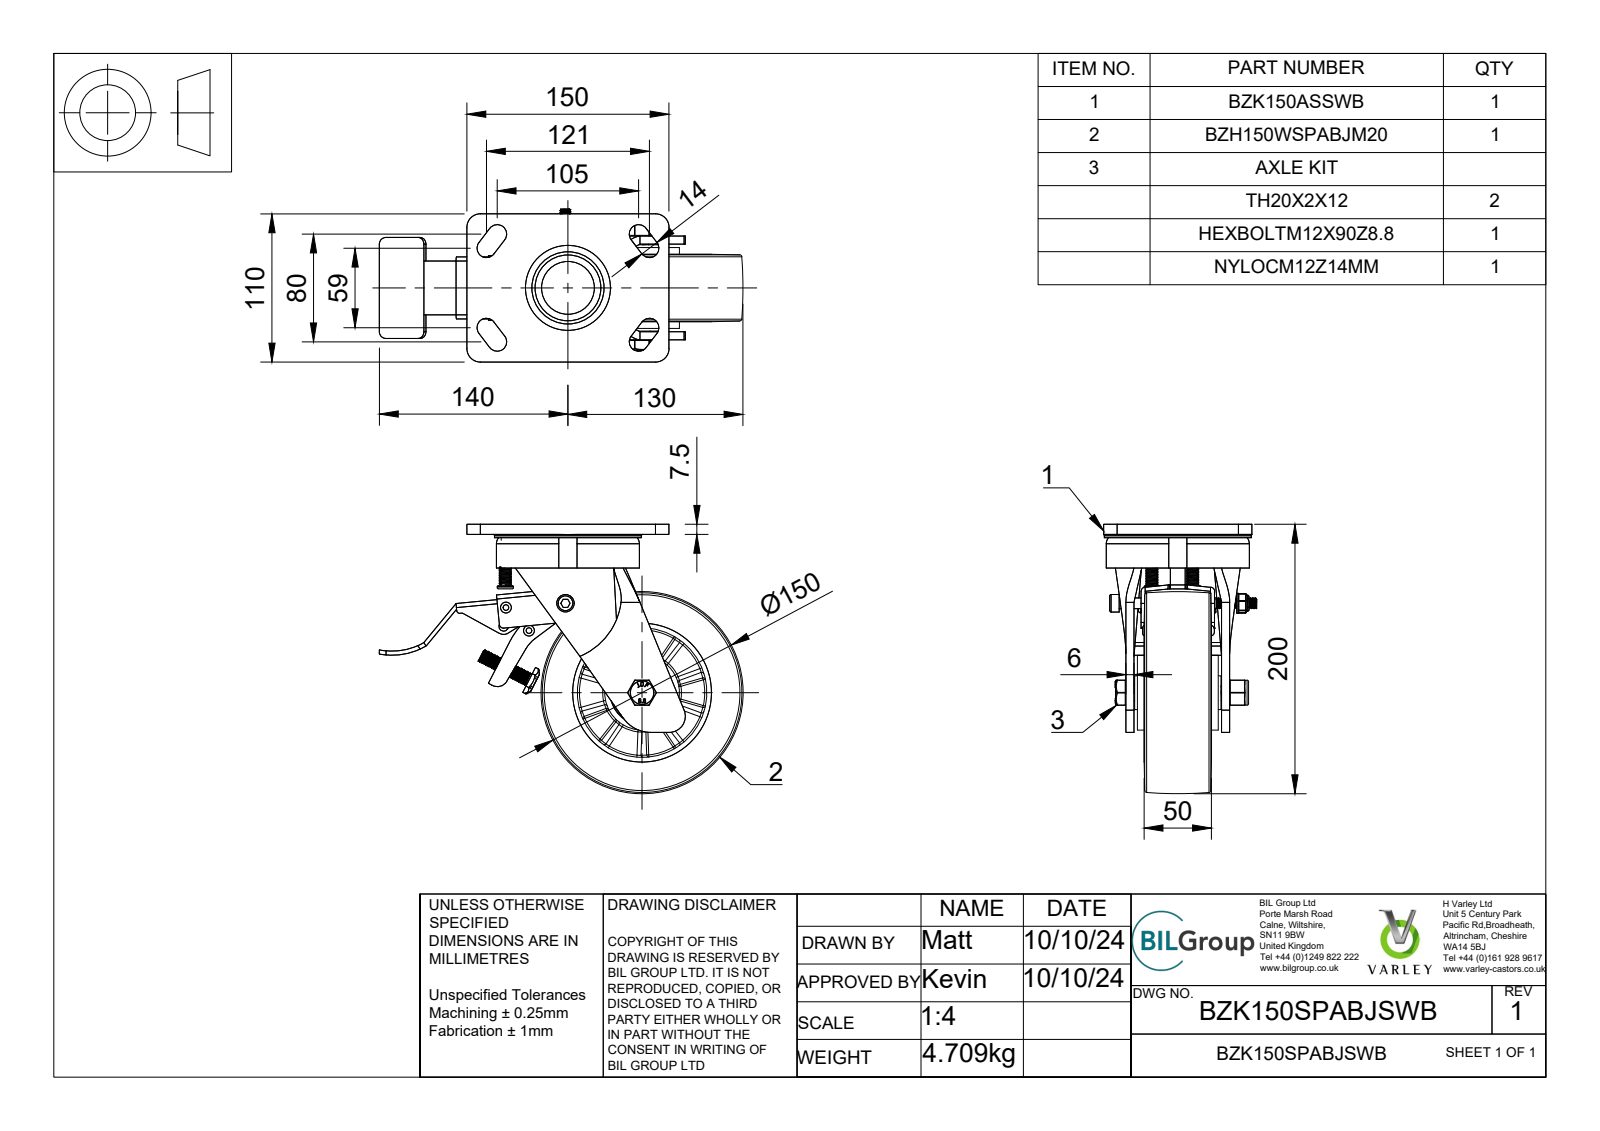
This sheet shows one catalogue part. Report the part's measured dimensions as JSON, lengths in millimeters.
{"part_name": "BZK150SPABJSWB v5; BZK150ASSWB v2; FABRICATED STEEL TOP PLATE; FABRICATED STEEL FORKS (+8 more)", "step_written_by": "Autodesk Translation Framework v13.20.0.188 (AUTOMOTIVE_DESIGN)", "units": "millimeters", "bodies": {"solids": 64, "faces": 2052, "planar": 747, "cylindrical": 516, "other": 789}, "overall_size": [270, 200, 114], "volume_mm3": 1542000, "surface_area_mm2": 489569, "round_holes": [[6, 5], [14, 2], [8, 1], [10, 1], [12, 1], [12.2, 1], [13, 1], [20, 1], [28.5, 1], [30.8, 1], [40.3, 1], [40.5, 1]], "round_bosses_or_shafts": [[6, 4], [12, 3], [8, 2], [109, 1], [107, 1], [55.5, 1], [40.8, 1], [31.3, 1]], "partial_cylinders_radius": [[0.5, 43], [7, 8], [3, 7], [0.47, 4], [0.9, 4], [5, 4], [10, 4], [0.89, 2]], "face_to_face_distances": [7.5, 71, 6, 25, 32.5, 3, 12.5, 8.25, 22.5, 11.25], "hole_center_spacings": [47.5, 14.08, 19.02, 24.19, 30, 33.94, 44.37, 49.04]}
